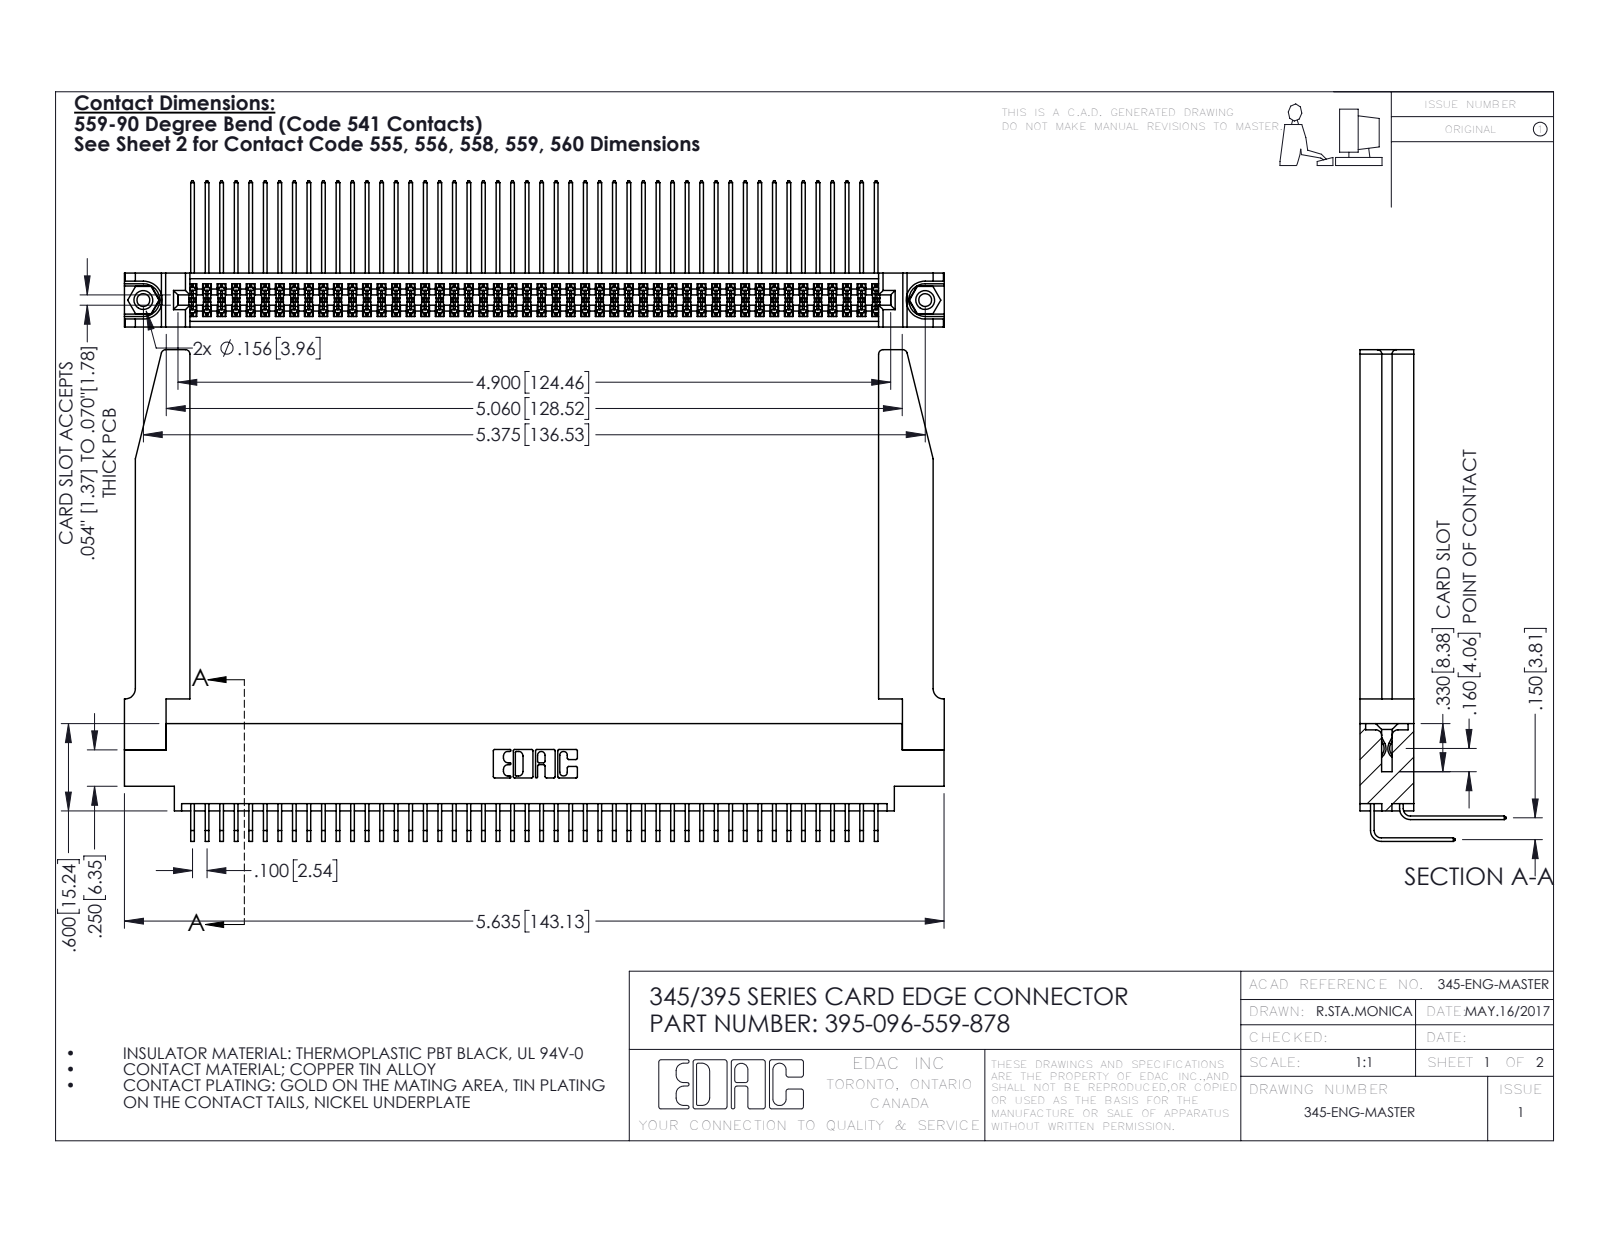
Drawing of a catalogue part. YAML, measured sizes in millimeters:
part_name: "345-292-001_558 559 Tail - 1; 345-292-001_559 Tail - 2; 345-250-001_345-250-001-102; 345 Part_0.170 Offset - 0.156 Dia-TH (+2 more)"
step_written_by: "SolidWorks 2016 (CONFIG_CONTROL_DESIGN)"
units: millimeters
bodies: {solids: 101, faces: 5356, planar: 3586, cylindrical: 1718, other: 52}
overall_size: [143.2, 85.8, 25.5]
volume: 22170
surface_area: 30990
round_holes:
  - {diameter: 2.3, count: 2}
  - {diameter: 3.2, count: 2}
  - {diameter: 4, count: 2}
  - {diameter: 1.6, count: 1}
round_bosses_or_shafts:
  - {diameter: 3.9, count: 2}
partial_cylinders:
  - {radius: 0.2, count: 145}
  - {radius: 0.3, count: 22}
  - {radius: 0.8, count: 8}
  - {radius: 0.2, count: 6}
  - {radius: 0.8, count: 6}
  - {radius: 0.7, count: 3}
  - {radius: 0.4, count: 2}
  - {radius: 0.5, count: 2}
face_to_face_distances: [9.4, 1.8, 7.6, 2.5, 6.9, 0.6, 5.1, 5.7, 3.8, 4.4]
hole_center_spacings: [6.9, 130.5, 136.5]
